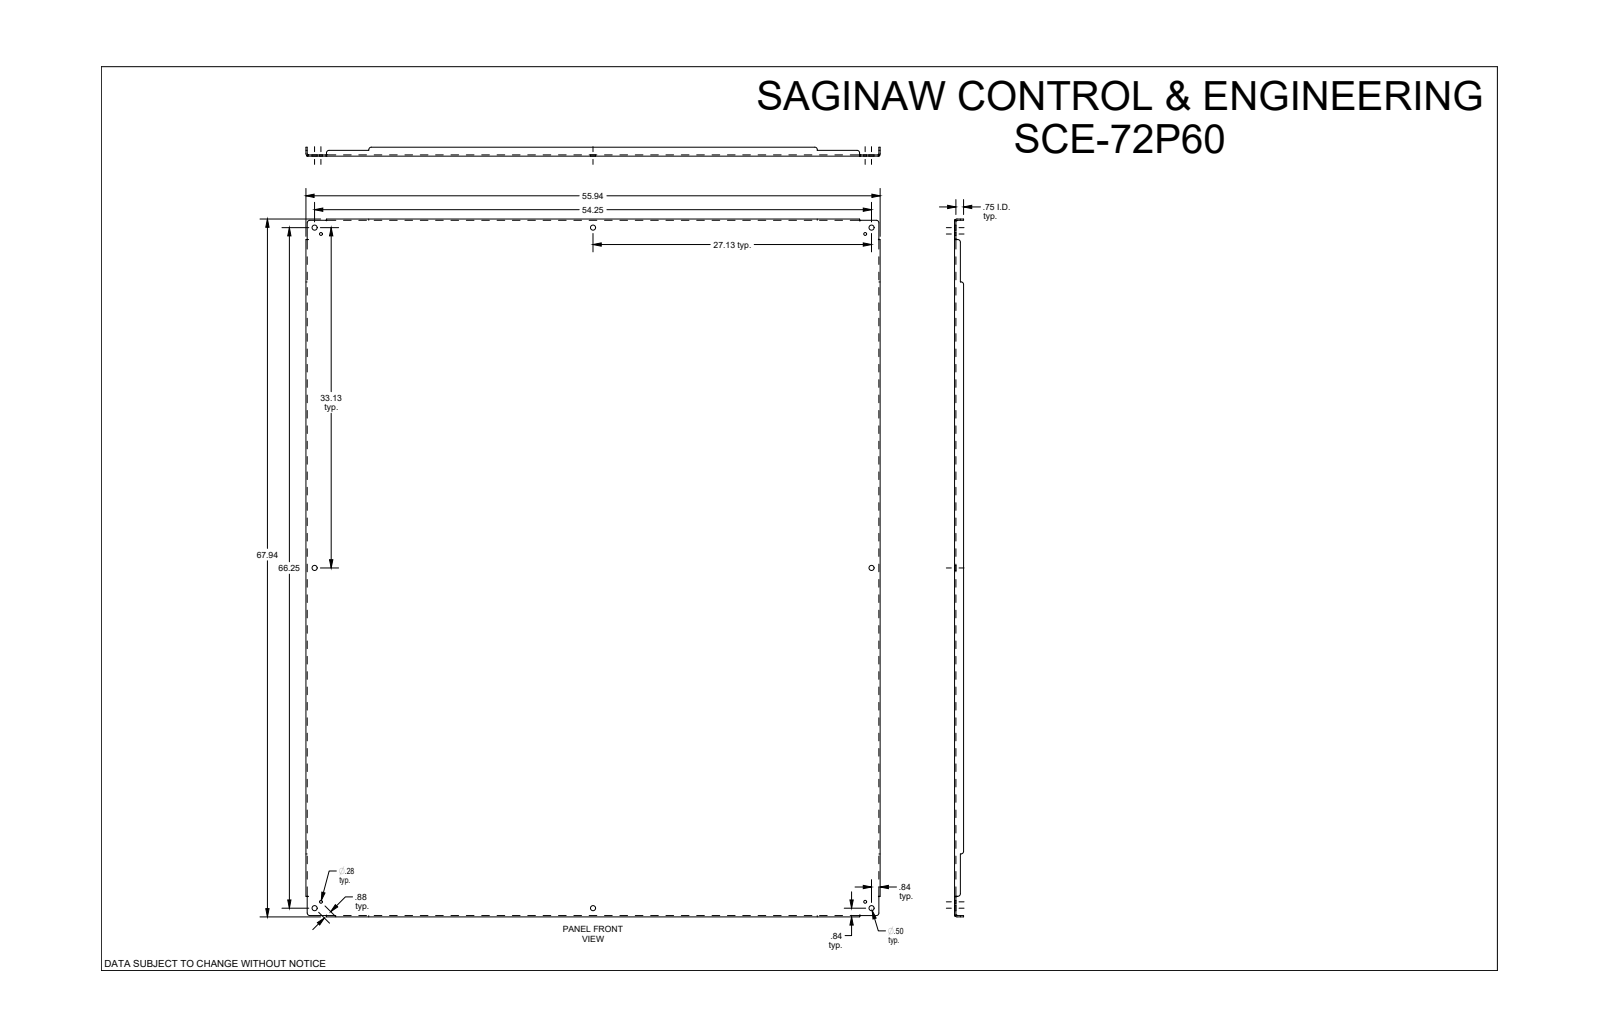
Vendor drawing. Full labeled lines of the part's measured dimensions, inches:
Part name (STEP PRODUCT): SCE-72P60
STEP written by: SolidWorks 2019 (CONFIG_CONTROL_DESIGN)
Units: inches
Bodies: 1 solid, 110 faces (46 planar, 40 cylindrical, 24 other)
Overall size (bounding box): 67.938 × 55.938 × 0.875
Volume: 492.8 in³ · Surface area: 7 918 in²
Round holes (diameter × count): ⌀0.5 ×8, ⌀0.281 ×4
Partial cylindrical surfaces — rounded edges, fillets, slot ends (radius × count): R0.25 ×12, R0.112 ×4, R0.237 ×4
Main face-to-face distances: 0.125, 0.125, 55.813, 67.813, 55.687, 55.938, 67.687, 67.938, 0.75, 0.875
Hole centre spacings: 0.875, 26.513, 27.125, 32.512, 33.125, 42.814, 53.635, 62.713
